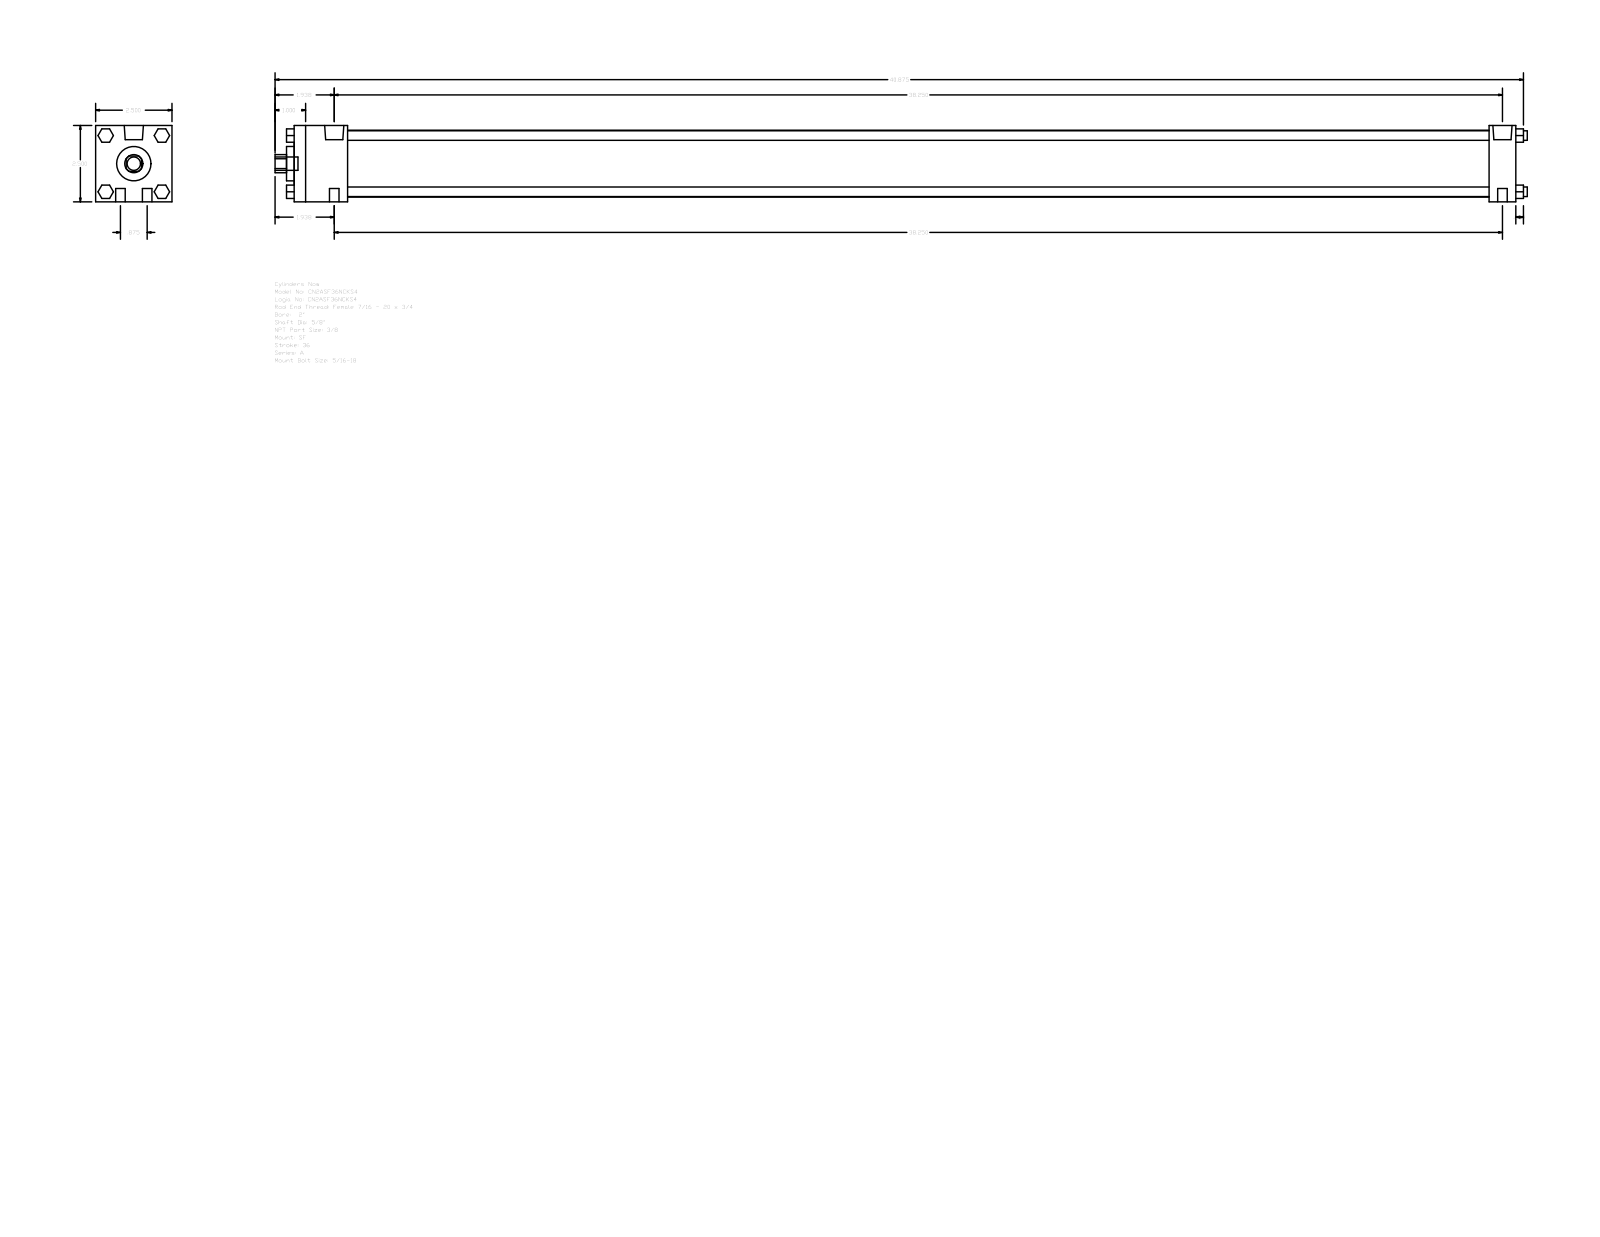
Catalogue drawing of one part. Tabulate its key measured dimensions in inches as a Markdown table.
| quantity | value |
| --- | --- |
| part name | A_SF__0200_0.625 |
| STEP written by | GSSL Pune (CONFIG_CONTROL_DESIGN) |
| units | inches |
| bodies | 0 solids, 124 faces (94 planar, 30 cylindrical, 0 other) |
| overall size | 41 × 2.5 × 2.5 |
| round holes (diameter × count) | 0.625 × 1, 1.125 × 1, 2.19 × 1 |
| round bosses / shafts (diameter × count) | 0.313 × 8, 0.627 × 2, 0.219 × 2, 0.437 × 1 |
| partial cylindrical surfaces (radius × count) | 0.297 × 1 |
| main face-to-face distances | 2.5, 40, 39.125, 0.875, 1.75, 37.375, 38.25, 2, 40.25, 0.25 |
